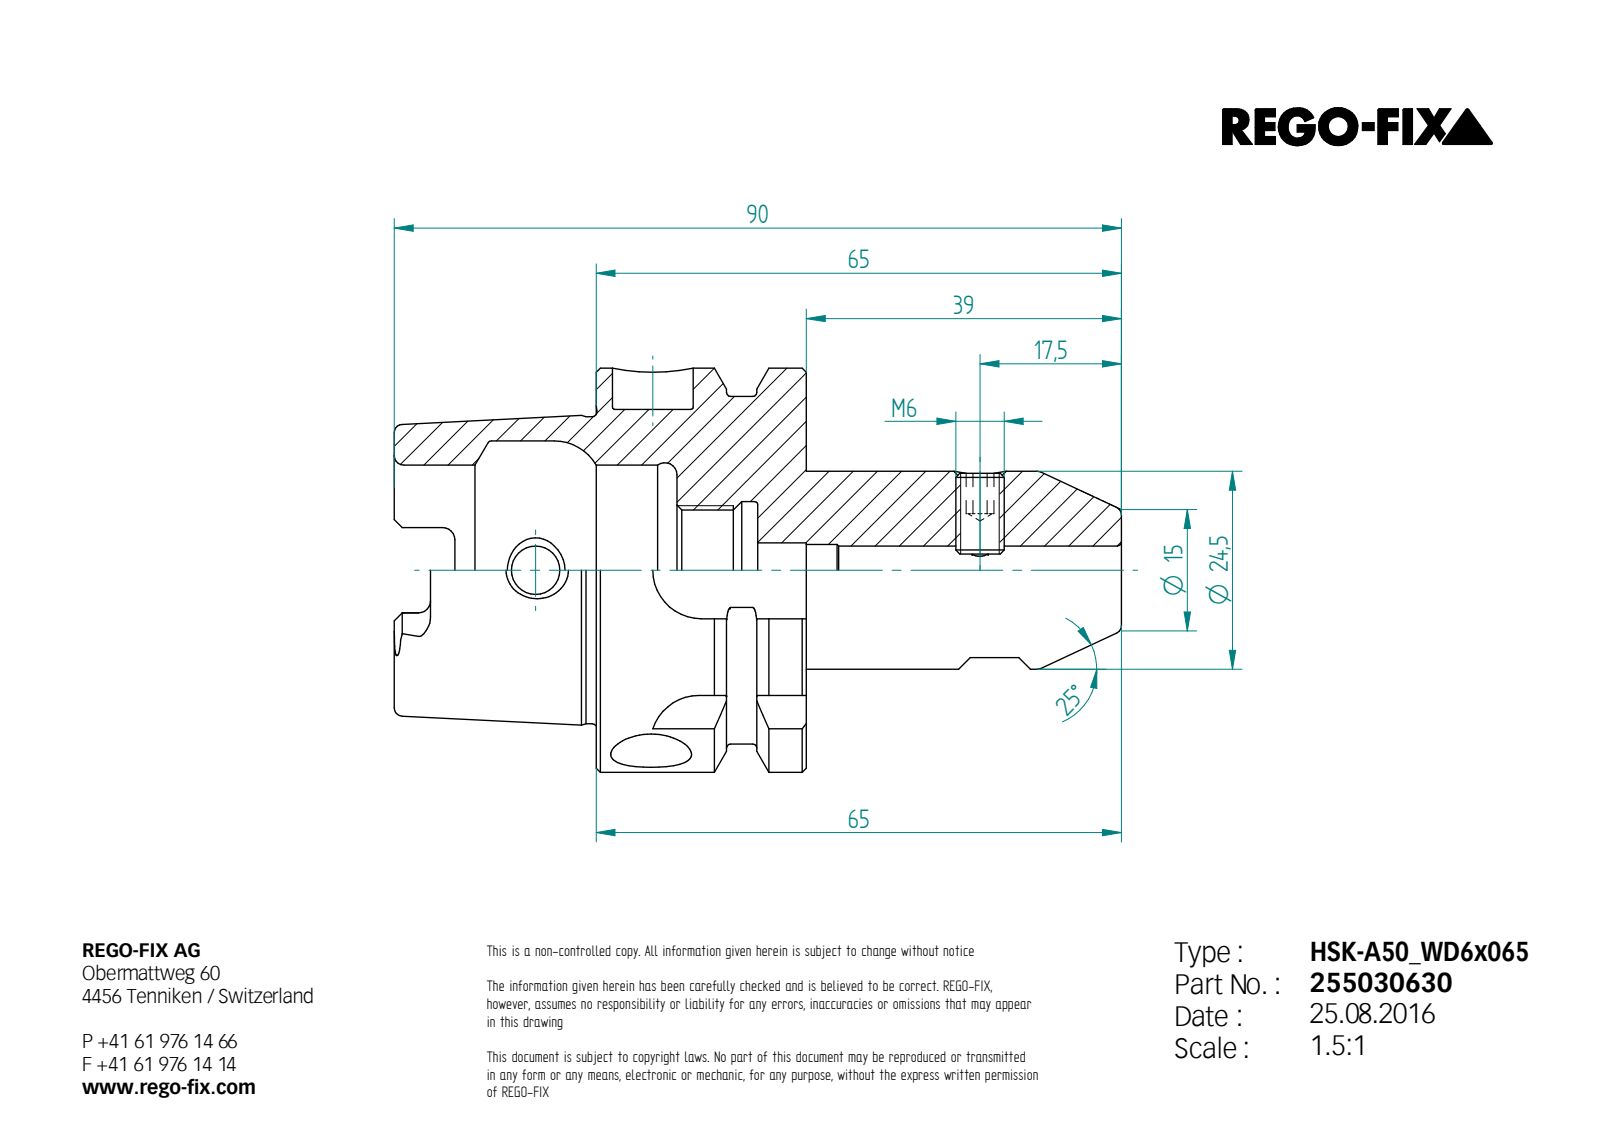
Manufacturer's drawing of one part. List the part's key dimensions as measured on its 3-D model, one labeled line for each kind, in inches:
STEP written by: Unknown (AUTOMOTIVE_DESIGN)
Units: inches
Bodies: 2 solids, 152 faces (64 planar, 36 cylindrical, 52 other)
Overall size (bounding box): 3.543 × 1.969 × 1.969
Volume: 3.914 in³ · Surface area: 29.38 in²
Round holes (diameter × count): ⌀0.236 ×2, ⌀0.394 ×2, ⌀0.194 ×1, ⌀0.252 ×1, ⌀0.268 ×1, ⌀0.587 ×1, ⌀0.669 ×1, ⌀1.024 ×1, ⌀1.26 ×1
Round bosses / shafts (diameter × count): ⌀1.969 ×1, ⌀1.693 ×1, ⌀1.496 ×1, ⌀0.965 ×1, ⌀0.236 ×1
Partial cylindrical surfaces — rounded edges, fillets, slot ends (radius × count): R0.059 ×6, R0.094 ×4, R0.236 ×4
Main face-to-face distances: 1.024, 0.394, 1.772, 0.63, 1.654, 0.984, 1.378, 2.008, 0.236, 0.787
Hole centre spacings: 1.594
